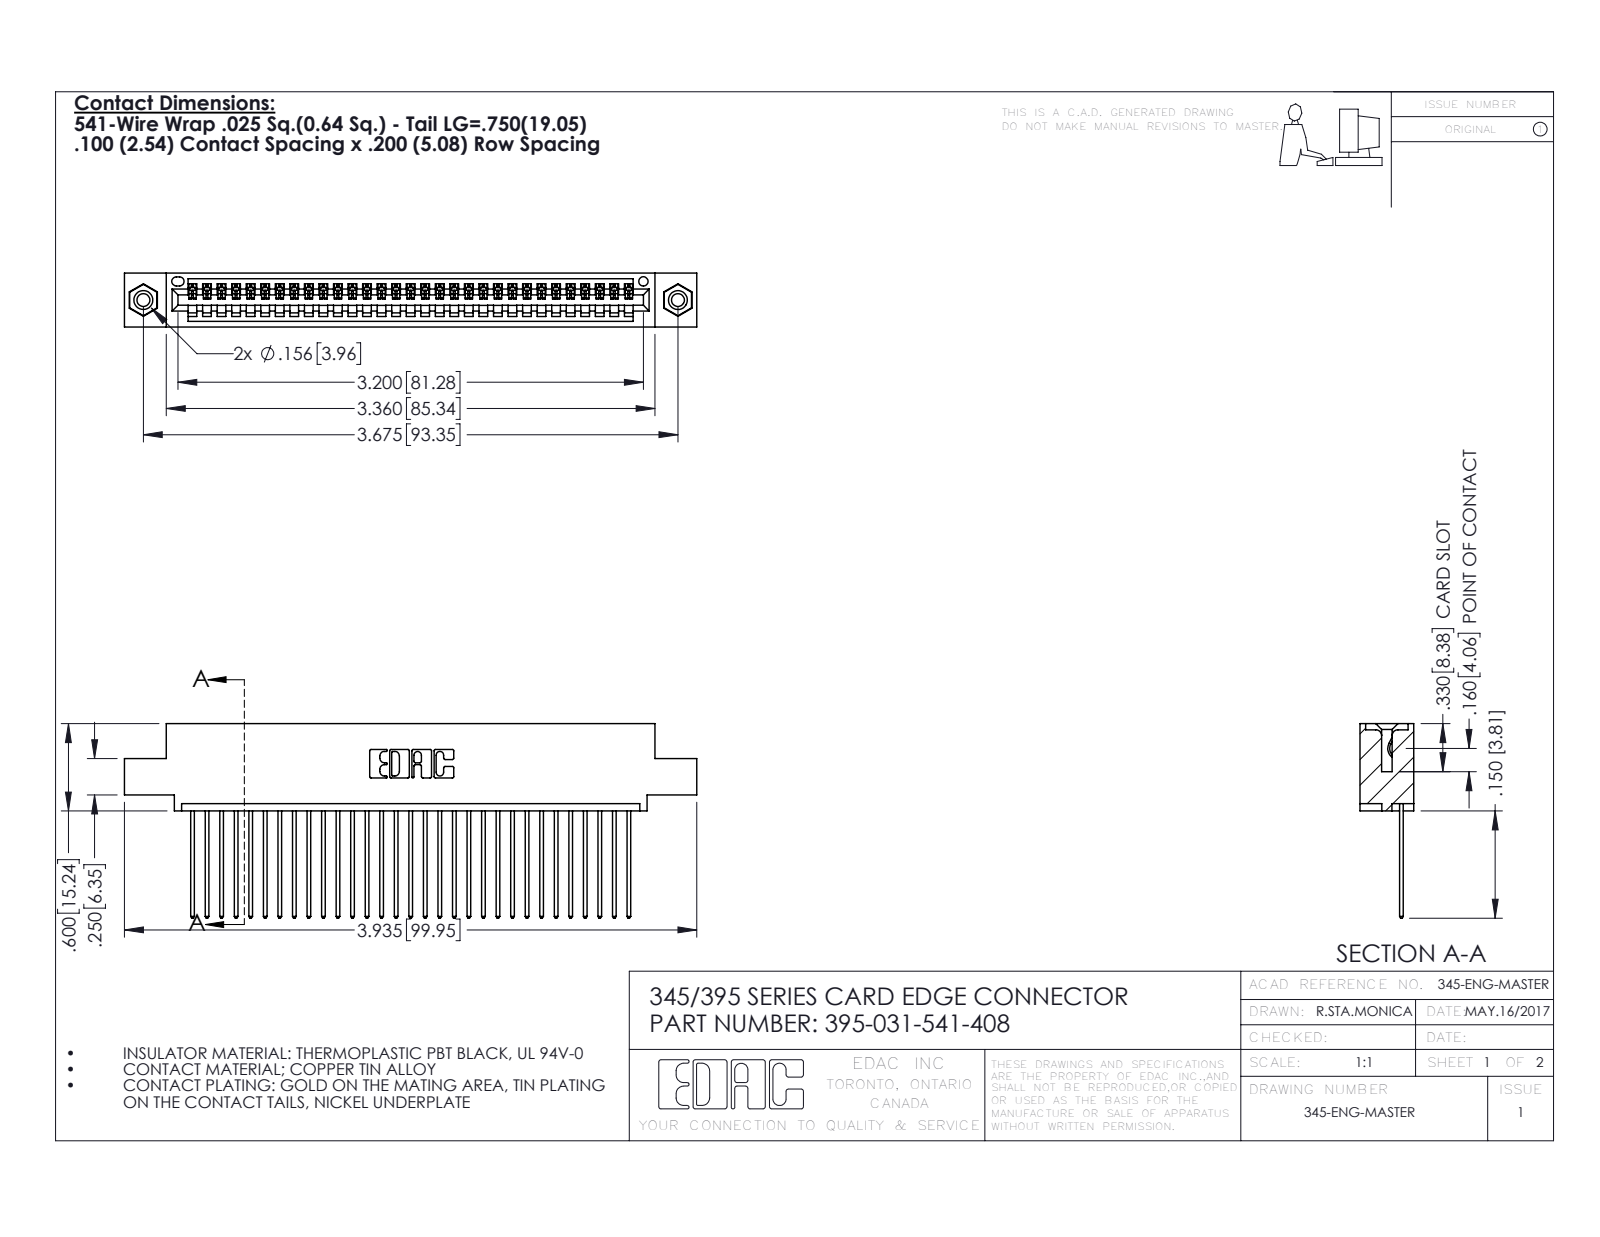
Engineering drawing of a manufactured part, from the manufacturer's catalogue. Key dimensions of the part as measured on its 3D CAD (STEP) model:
Part name (STEP PRODUCT): 395-031-541-408; 345-292-001_345-293-141; 345 Part_0.110 Offset - 0.156 Dia-TI; 345-250-001_345-250-003-102
STEP written by: SolidWorks 2016 (CONFIG_CONTROL_DESIGN)
Units: inches
Bodies: 34 solids, 1988 faces (1356 planar, 616 cylindrical, 16 other)
Overall size (bounding box): 3.935 × 1.337 × 0.37
Volume: 0.575 in³ · Surface area: 20.27 in²
Round holes (diameter × count): ⌀0.089 ×2, ⌀0.125 ×2, ⌀0.156 ×2, ⌀0.064 ×1
Round bosses / shafts (diameter × count): ⌀0.155 ×2
Partial cylindrical surfaces — rounded edges, fillets, slot ends (radius × count): R0.006 ×62, R0.01 ×62, R0.01 ×22, R0.007 ×6, R0.031 ×6, R0.026 ×3, R0.031 ×2, R0.04 ×2
Main face-to-face distances: 0.072, 0.298, 0.098, 0.272, 0.025, 0.37, 0.2, 0.225, 0.149, 0.072
Hole centre spacings: 0.27, 3.44, 3.675
